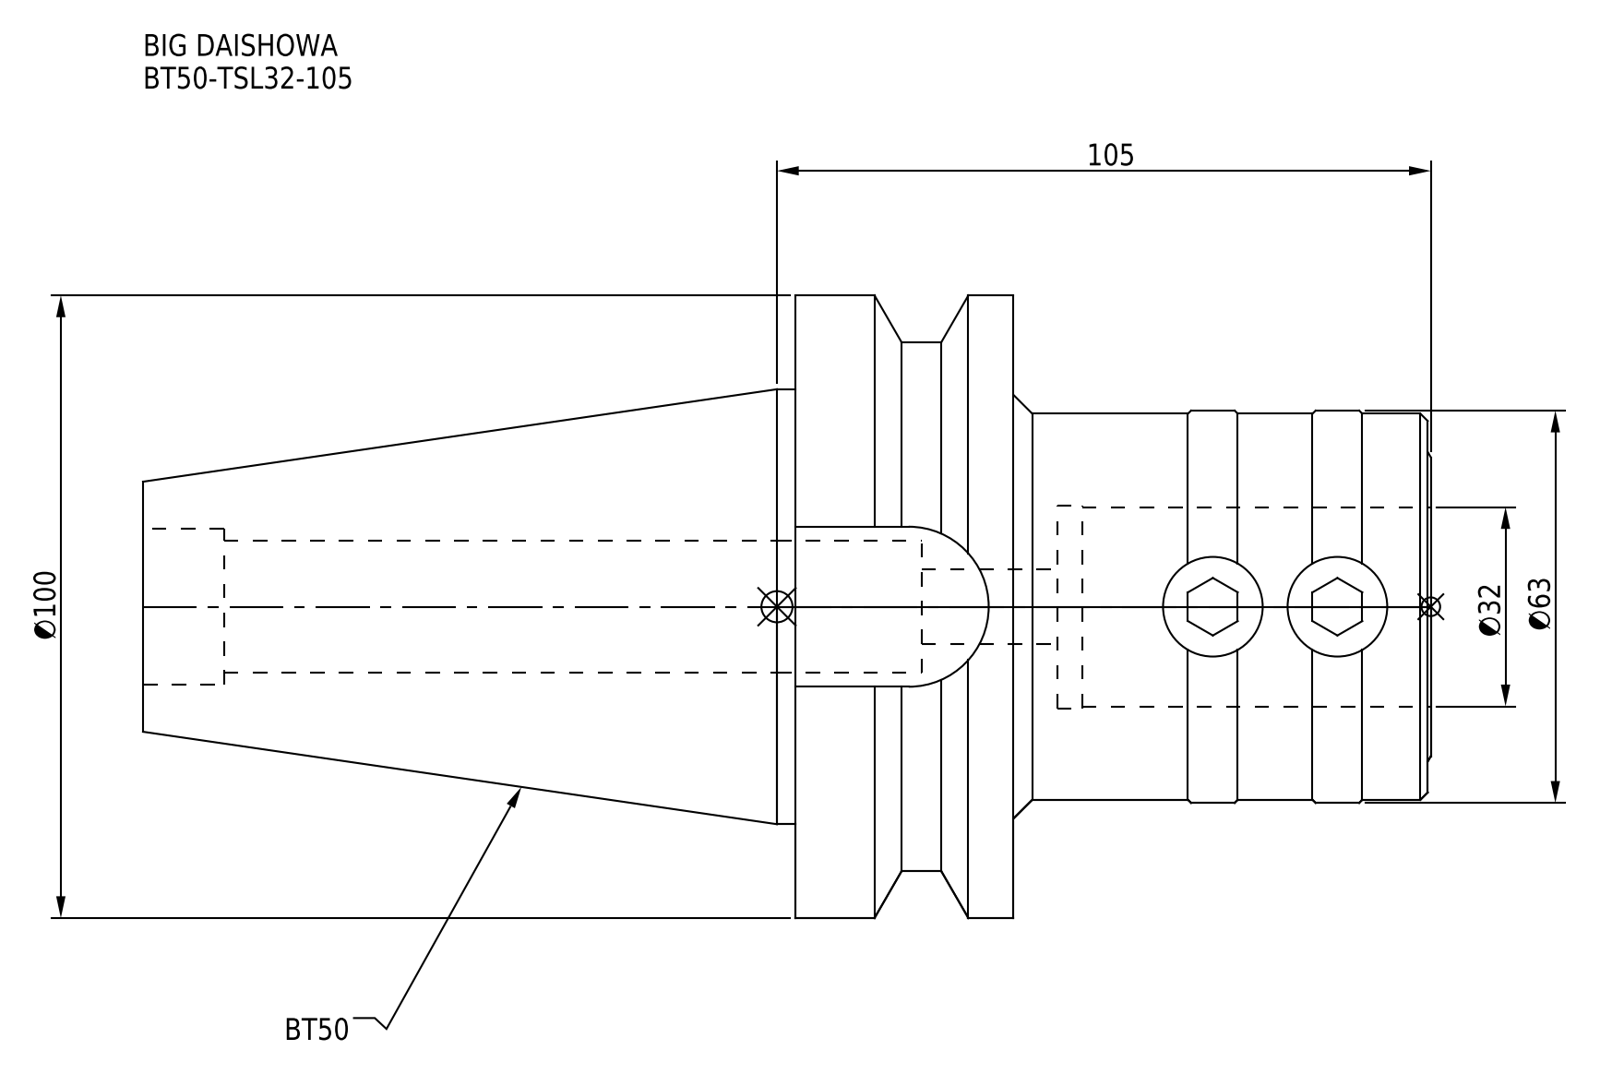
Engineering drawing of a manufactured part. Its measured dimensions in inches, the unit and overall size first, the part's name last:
Units: inches
Overall size (bounding box): 8.142 × 3.937 × 3.937
Round holes (diameter × count): ⌀0.472 ×1, ⌀0.835 ×1, ⌀0.984 ×1, ⌀1.26 ×1, ⌀1.283 ×1
Round bosses / shafts (diameter × count): ⌀3.937 ×1, ⌀3.346 ×1, ⌀2.75 ×1, ⌀2.48 ×1, ⌀2.441 ×1
Partial cylindrical surfaces — rounded edges, fillets, slot ends (radius × count): R0.506 ×1
Main face-to-face distances: 1.378, 2.638, 4.016, 0.02, 2.618, 3.996, 8.142, 8.122, 5.504, 4.126
Volume: 36.69 in³ · Surface area: 113.2 in²
Bodies: 1 solid, 67 faces (15 planar, 32 cylindrical, 20 other)
Part name (STEP PRODUCT): BT50-TSL32-105
STEP written by: CREO PARAMETRIC BY PTC INC, 2016380 (AUTOMOTIVE_DESIGN)
